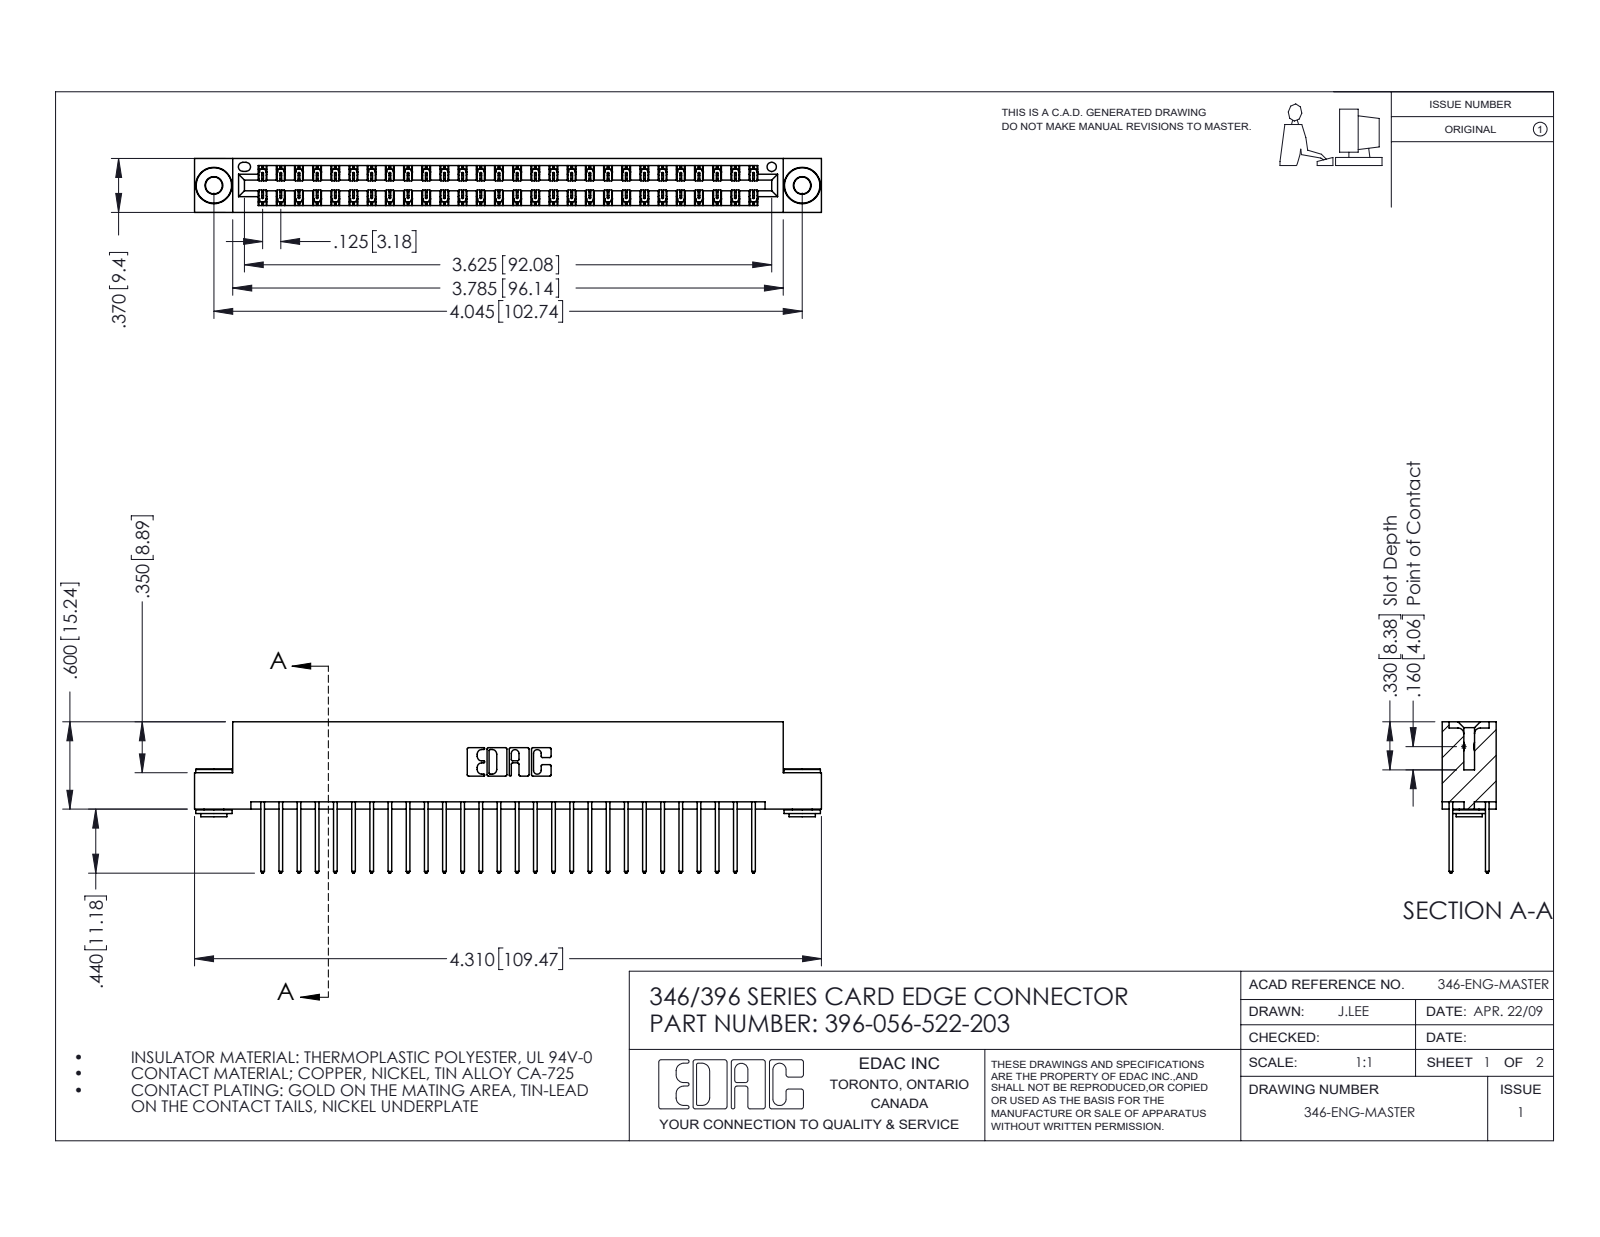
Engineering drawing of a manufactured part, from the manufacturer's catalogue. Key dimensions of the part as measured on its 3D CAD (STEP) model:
Part name (STEP PRODUCT): 396-056-522-203; 345-250-002_345-250-002-102; 345-292-001_345-293-122; 346 Part_Flush Mounting Lugs - 0.156 Dia-TH
STEP written by: SolidWorks 2016 (CONFIG_CONTROL_DESIGN)
Units: inches
Bodies: 59 solids, 3072 faces (2046 planar, 1018 cylindrical, 8 other)
Overall size (bounding box): 4.31 × 1.04 × 0.37
Volume: 0.655 in³ · Surface area: 23.88 in²
Round holes (diameter × count): ⌀0.116 ×2, ⌀0.156 ×2, ⌀0.064 ×1
Round bosses / shafts (diameter × count): ⌀0.25 ×2, ⌀0.18 ×2, ⌀0.136 ×2
Partial cylindrical surfaces — rounded edges, fillets, slot ends (radius × count): R0.006 ×84, R0.01 ×56, R0.01 ×22, R0.007 ×6, R0.031 ×6, R0.026 ×3, R0.014 ×2, R0.022 ×2
Main face-to-face distances: 0.048, 0.322, 0.25, 0.37, 0.025, 0.072, 0.298, 0.275, 0.148, 0.222
Hole centre spacings: 0.246, 3.837, 4.045
